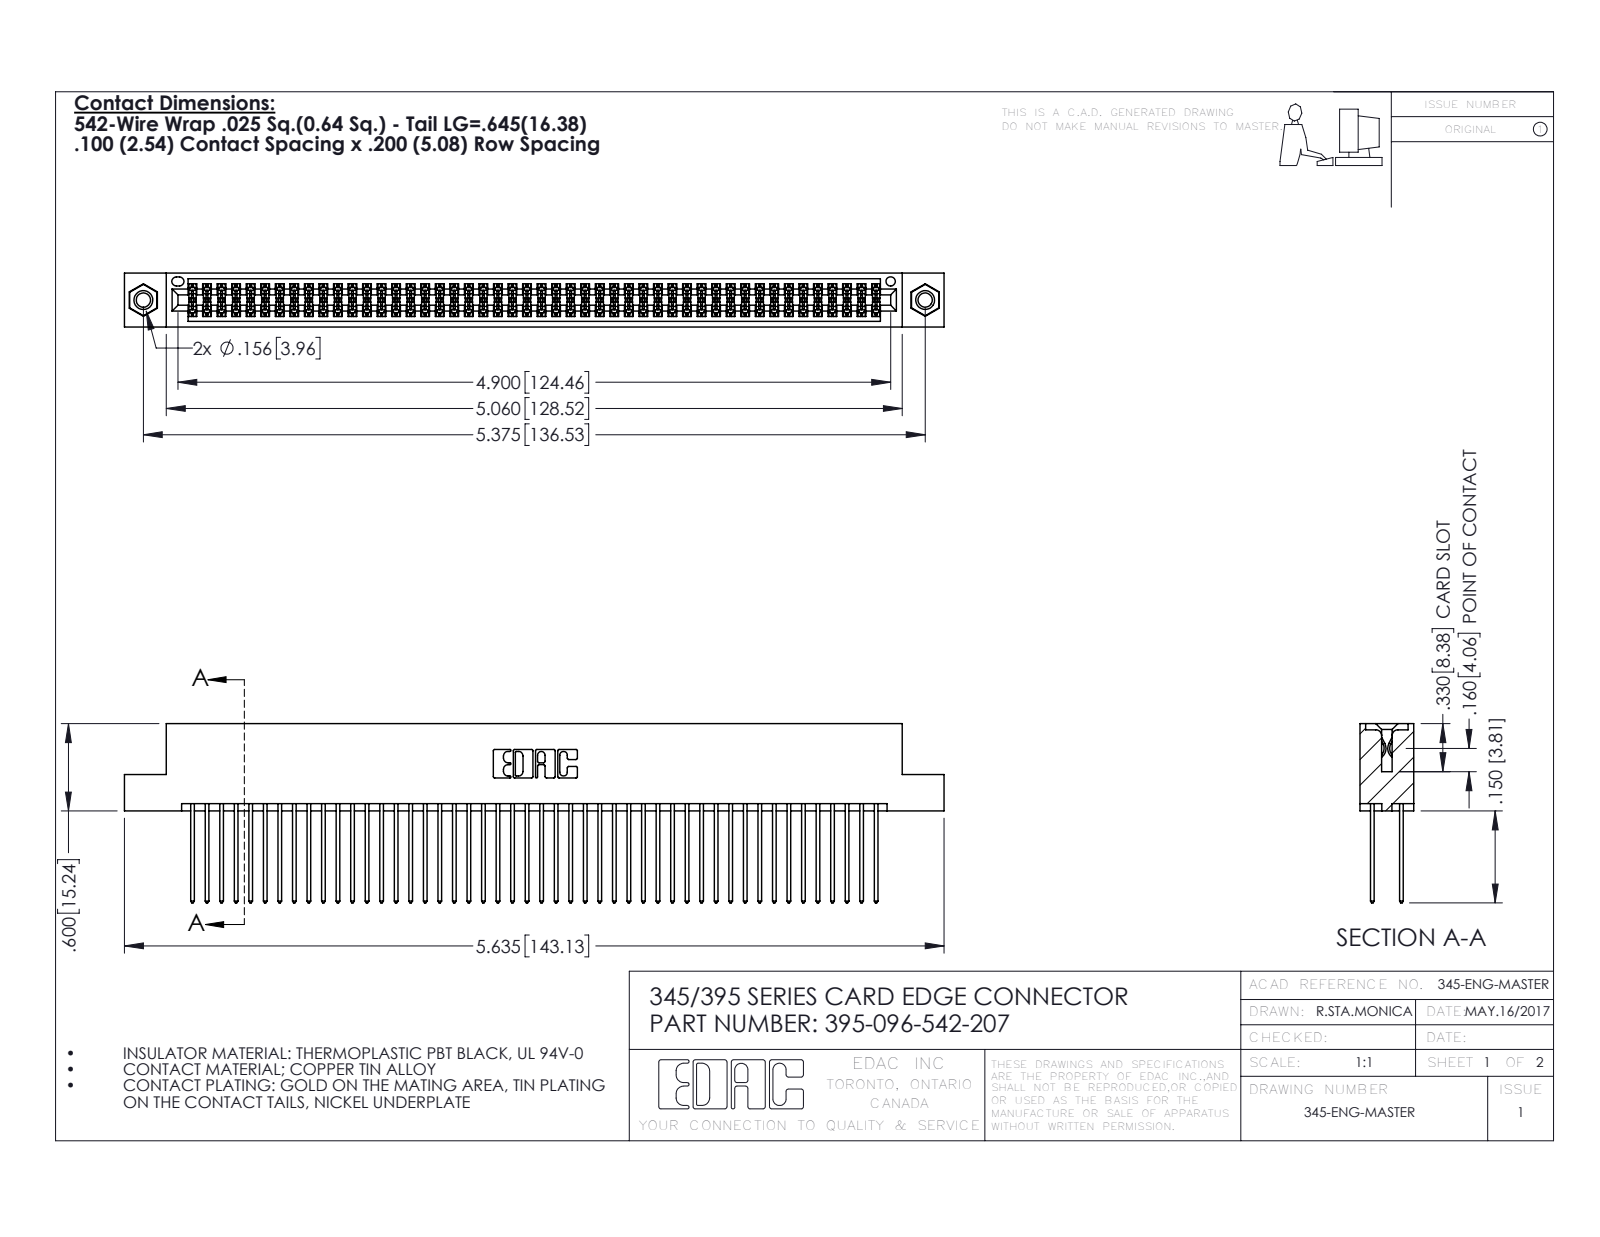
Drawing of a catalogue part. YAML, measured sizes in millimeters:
part_name: "395-096-542-207; 345 Part_Flush Mounting Lugs - 0.156 Dia-TI; 345-292-001_345-293-142; 345-250-001_345-250-005-103"
step_written_by: "SolidWorks 2016 (CONFIG_CONTROL_DESIGN)"
units: millimeters
bodies: {solids: 99, faces: 4986, planar: 3280, cylindrical: 1690, other: 16}
overall_size: [143.1, 31.3, 9.4]
volume: 14400
surface_area: 23510
round_holes:
  - {diameter: 2.5, count: 2}
  - {diameter: 3.2, count: 2}
  - {diameter: 4, count: 2}
  - {diameter: 1.6, count: 1}
round_bosses_or_shafts:
  - {diameter: 3.9, count: 2}
partial_cylinders:
  - {radius: 0.2, count: 144}
  - {radius: 0.3, count: 96}
  - {radius: 0.3, count: 22}
  - {radius: 0.2, count: 6}
  - {radius: 0.8, count: 6}
  - {radius: 0.7, count: 3}
  - {radius: 0.4, count: 2}
  - {radius: 0.5, count: 2}
face_to_face_distances: [1.8, 7.6, 5.1, 2.5, 6.9, 0.6, 5.7, 9.4, 4.4, 3.8]
hole_center_spacings: [6.9, 130.5, 136.5]
